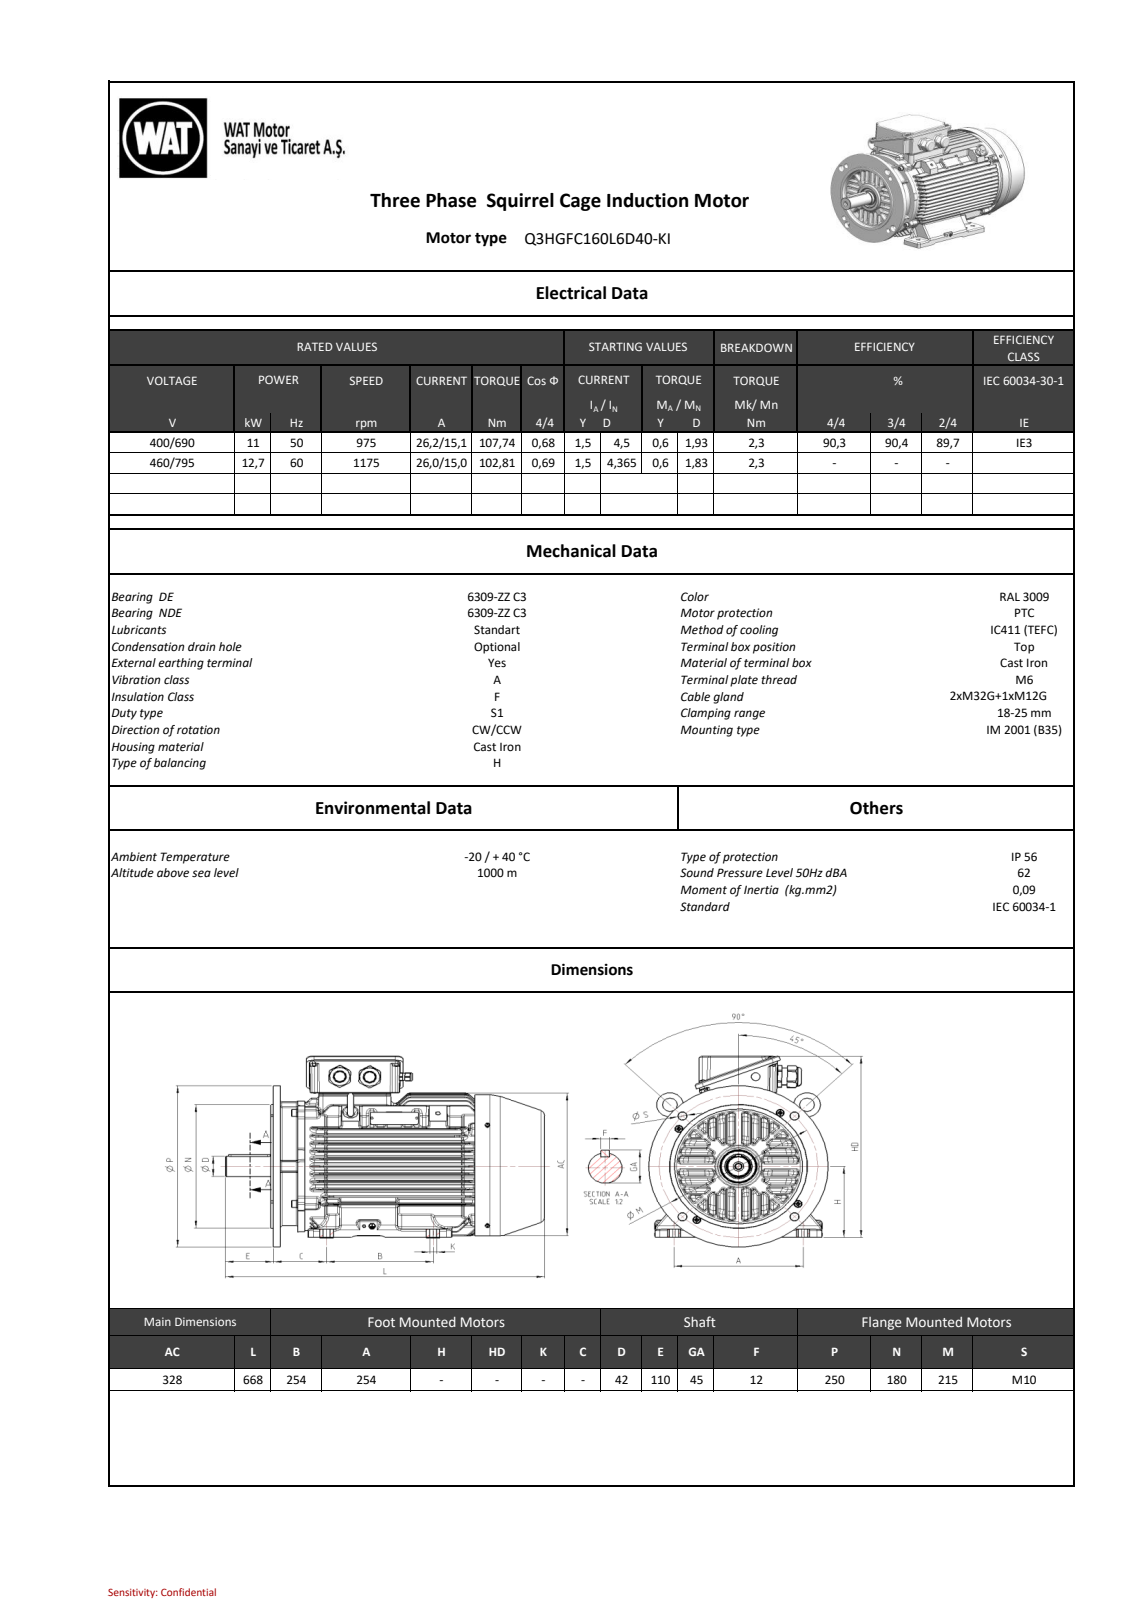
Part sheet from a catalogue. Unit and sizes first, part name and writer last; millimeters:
Units: millimetres
Overall size (bounding box): 667.5 × 391.09 × 327.37
Round holes (diameter × count): ⌀8.5 ×12, ⌀5.5 ×8, ⌀4.2 ×6, ⌀10.3 ×6, ⌀5.3 ×4, ⌀2.5 ×2, ⌀6.8 ×2, ⌀19 ×2, ⌀21 ×2, ⌀10 ×1, ⌀14 ×1, ⌀17 ×1
Round bosses / shafts (diameter × count): ⌀16 ×8, ⌀10 ×8, ⌀20 ×4, ⌀36 ×2, ⌀34.5 ×2, ⌀31.25 ×2, ⌀30 ×2, ⌀317 ×1
Partial cylindrical surfaces — rounded edges, fillets, slot ends (radius × count): R5 ×247, R3 ×118, R1.5 ×112, R2 ×68, R4 ×66, R1.8 ×54, R1 ×35, R0.4 ×28
Main face-to-face distances: 15.17, 137.45, 30.42, 122.2, 15.25, 45.73, 106.89, 30.56, 15.31, 61.11
Hole centre spacings: 136, 42.46, 144, 164.06, 194.08, 203.65, 250.56, 85.59
Bodies: 0 solids, 5243 faces (1058 planar, 1452 cylindrical, 2733 other)
Part name (STEP PRODUCT): C9017F38B806swrj
STEP written by: SIEMENS PLM Software NX 11.0 (AUTOMOTIVE_DESIGN)
